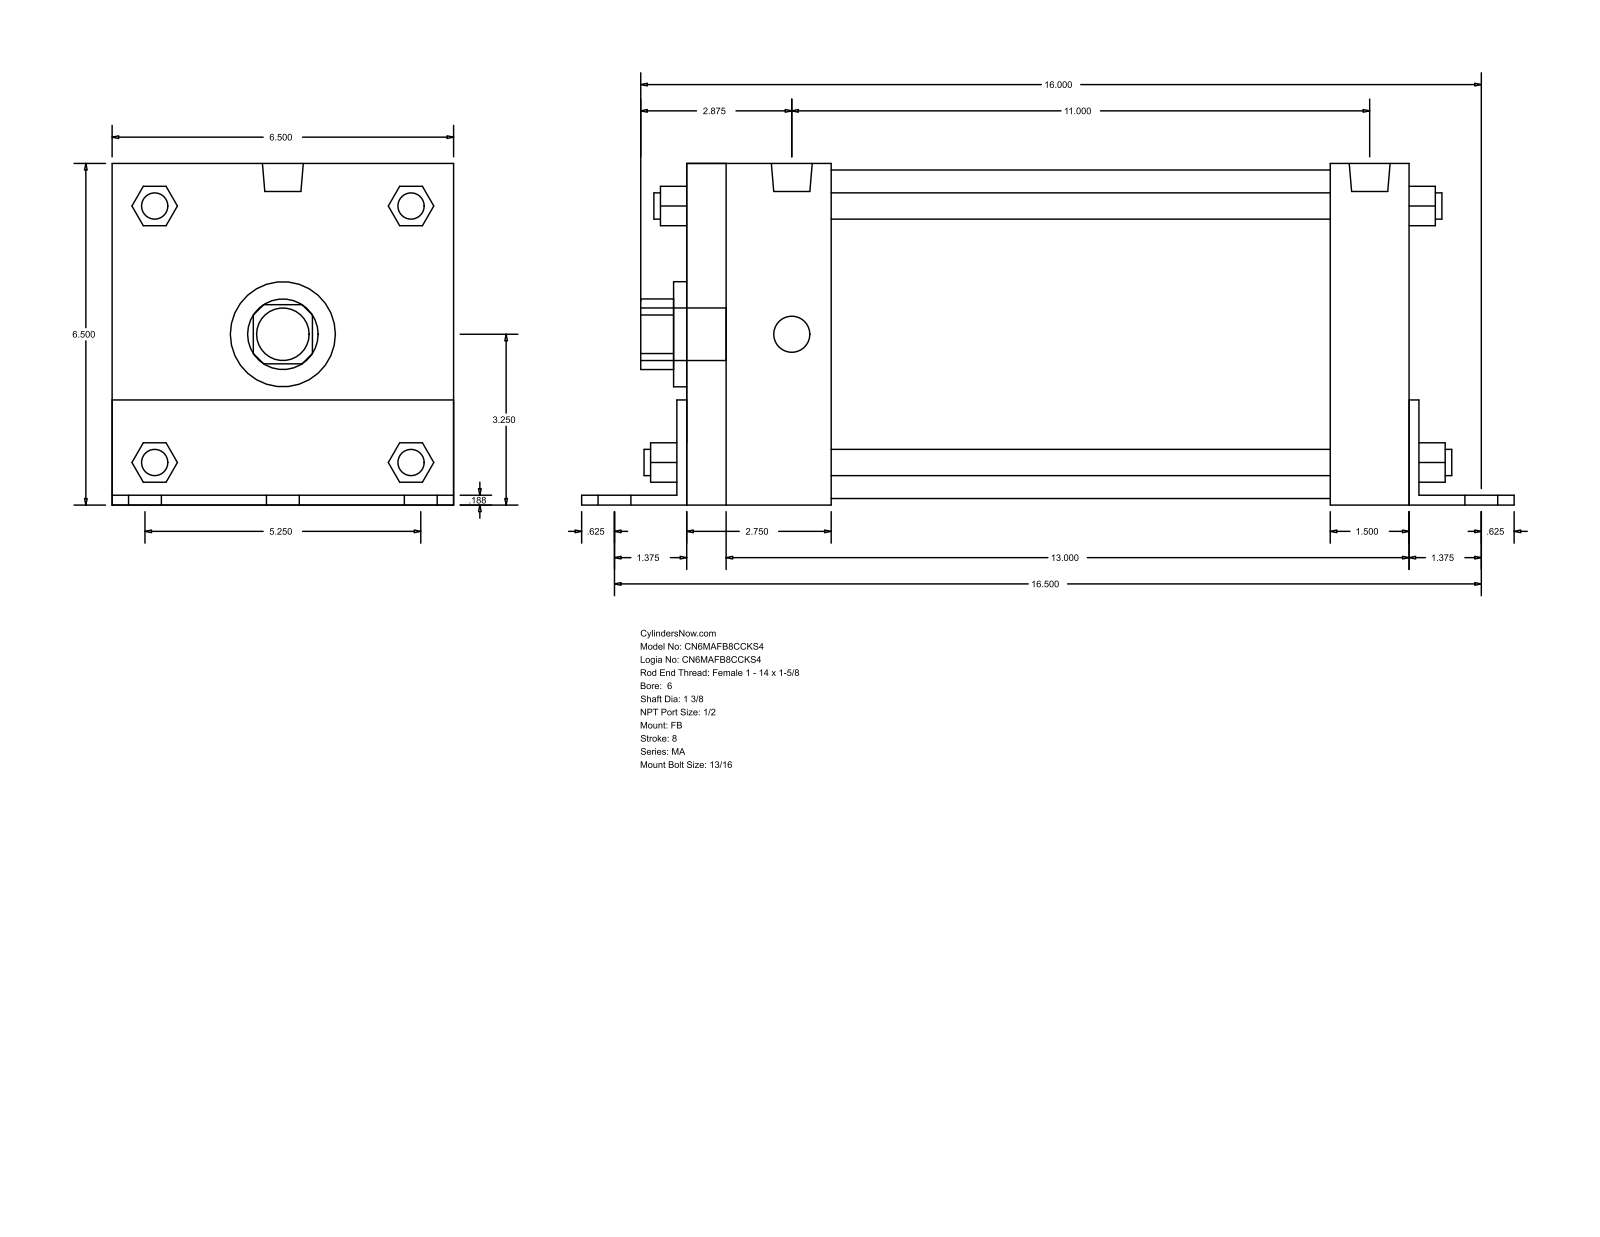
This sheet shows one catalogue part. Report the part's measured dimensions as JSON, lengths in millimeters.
{"part_name": "MA_FB__0600_1.375", "step_written_by": "GSSL Pune (CONFIG_CONTROL_DESIGN)", "units": "millimeters", "bodies": {"solids": 0, "faces": 140, "planar": 105, "cylindrical": 35, "other": 0}, "overall_size": [447.68, 165.15, 165.1], "round_holes": [[34.92, 1], [50.8, 1], [158.75, 1]], "round_bosses_or_shafts": [[20.64, 6], [17.46, 4], [12.7, 4], [19.77, 2], [25.4, 1]], "partial_cylinders_radius": [[17.06, 1], [32.05, 1]], "face_to_face_distances": [165.1, 4.76, 346.07, 165.15, 4.71, 160.39, 4.77, 38.1, 350.84, 355.6]}
